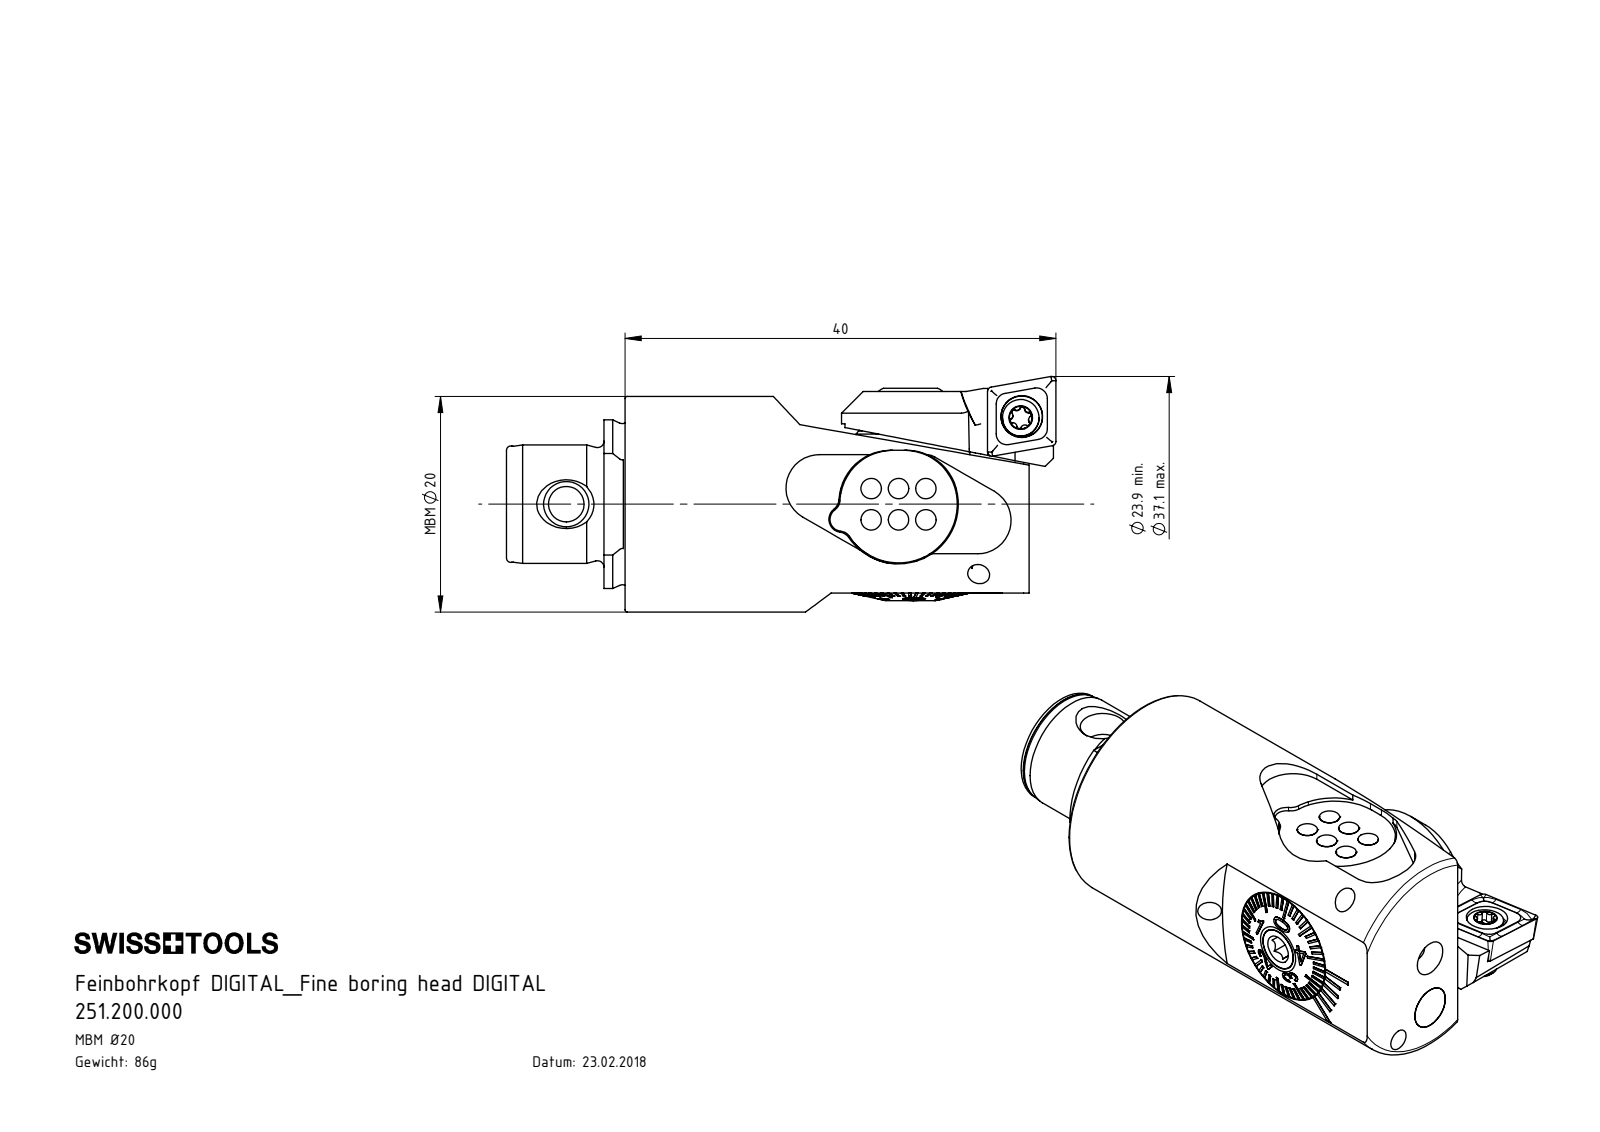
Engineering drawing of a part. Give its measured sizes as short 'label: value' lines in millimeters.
name: F20-BG3.004.017_A; F20-WCA.001.005_D_fertigbearbeitet; F20-BG1.DA2.011_Aktuell 06.2014-M1x2; MB1-F20.DA1.040_A (+8 more)
written by: SolidWorks 2017 (CONFIG_CONTROL_DESIGN)
unit: mm
bodies: 16 solids, 871 faces (371 planar, 192 cylindrical, 308 other)
size: 51 × 21.85 × 20
volume: 11 036 mm³; area: 8 121 mm²
holes: 6× ⌀2, 3× ⌀3.3, 1× ⌀0.7, 1× ⌀1.6, 1× ⌀1.9, 1× ⌀2.05, 1× ⌀2.4, 1× ⌀2.5, 1× ⌀2.8, 1× ⌀3, 1× ⌀3.85, 1× ⌀4
bosses: 6× ⌀1.9, 2× ⌀6, 2× ⌀4, 2× ⌀3.95, 1× ⌀20, 1× ⌀11, 1× ⌀10.98, 1× ⌀10.85
rounds: 6× R0.21, 5× R0.36, 3× R1.1, 3× R1.2, 3× R5, 2× R0.3, 2× R0.5, 2× R2
face distances: 15.05, 1.5, 2.8, 3.7, 11.35, 0.8, 1.4, 14.25, 2.9, 12.5
hole spacings: 1.14, 2.6, 3.51, 4.44, 5.6, 8.3, 14, 29.6
